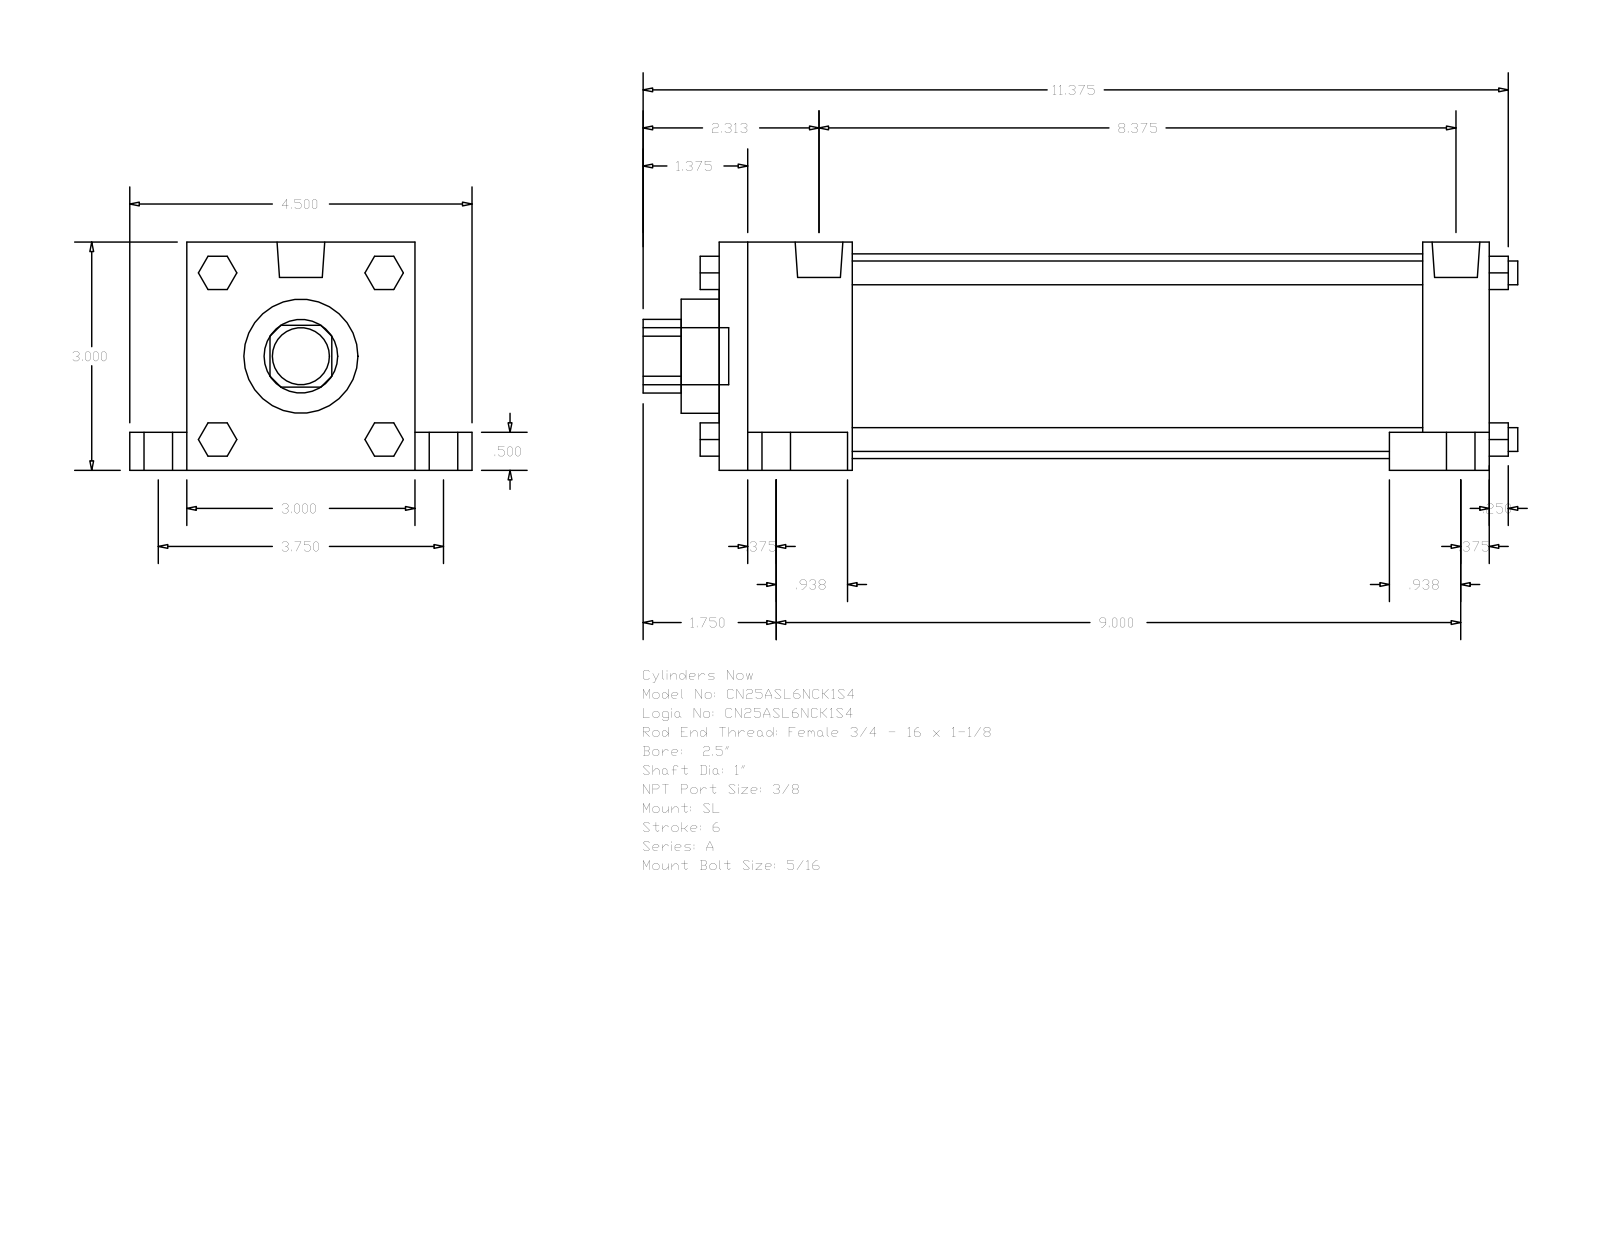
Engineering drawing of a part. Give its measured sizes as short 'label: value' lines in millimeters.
name: A_SL__0250_1
written by: GSSL Pune (CONFIG_CONTROL_DESIGN)
unit: mm
bodies: 0 solids, 148 faces (112 planar, 36 cylindrical, 0 other)
size: 292.1 × 114.3 × 76.2
holes: 1× ⌀25.4, 1× ⌀38.1, 1× ⌀68.33
bosses: 4× ⌀15.88, 4× ⌀9.53, 4× ⌀7.94, 4× ⌀5.56, 2× ⌀15.93, 1× ⌀19.05
rounds: 1× R12.29
face distances: 76.2, 257.17, 12.7, 22.22, 44.45, 212.72, 234.95, 190.5, 19.05, 63.5
